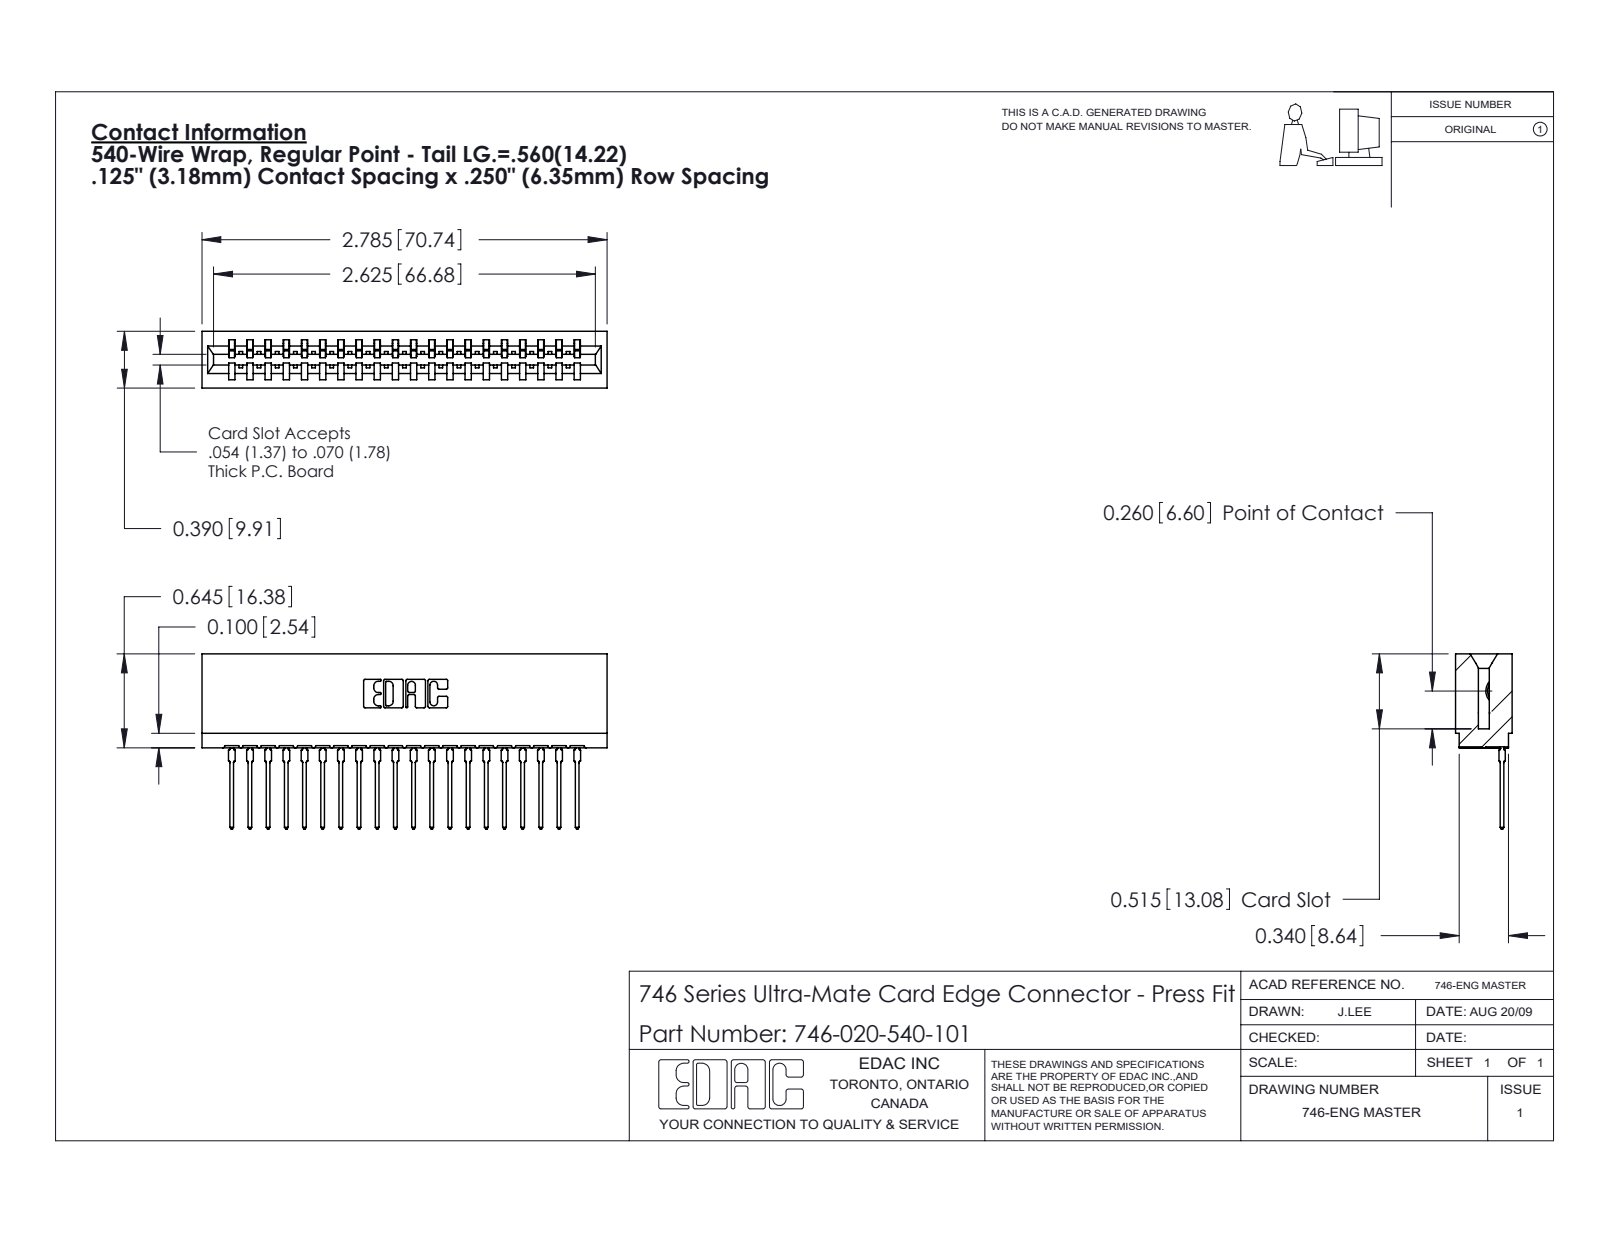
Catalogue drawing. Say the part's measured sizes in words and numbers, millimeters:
The part is named "746-020-540-101; 746-292-001_540; 746 Part_.515 Slot Depth - 01". Its 3-D file was written by "SolidWorks 2020 (CONFIG_CONTROL_DESIGN)". It is 21 solids with 2257 faces: 1315 planar, 422 cylindrical and 520 other. Overall it measures 70.7 by 30.6 by 9.9 millimeters. Its volume is 7 590 cubic millimeters and its surface area 11 120 square millimeters. Partial cylindrical surfaces (rounded edges, fillets, slot ends): 40 of radius 0.5, 22 of radius 0.3, 21 of radius 0.4, 6 of radius 0.2, 6 of radius 0.8, 4 of radius 0.1, 4 of radius 0.3, 3 of radius 0.7. The main face-to-face distances are 6.4, 1.4, 8.5, 9.9, 12.7, 0.6, 7.8, 2.1, 9.5, 3.2.
